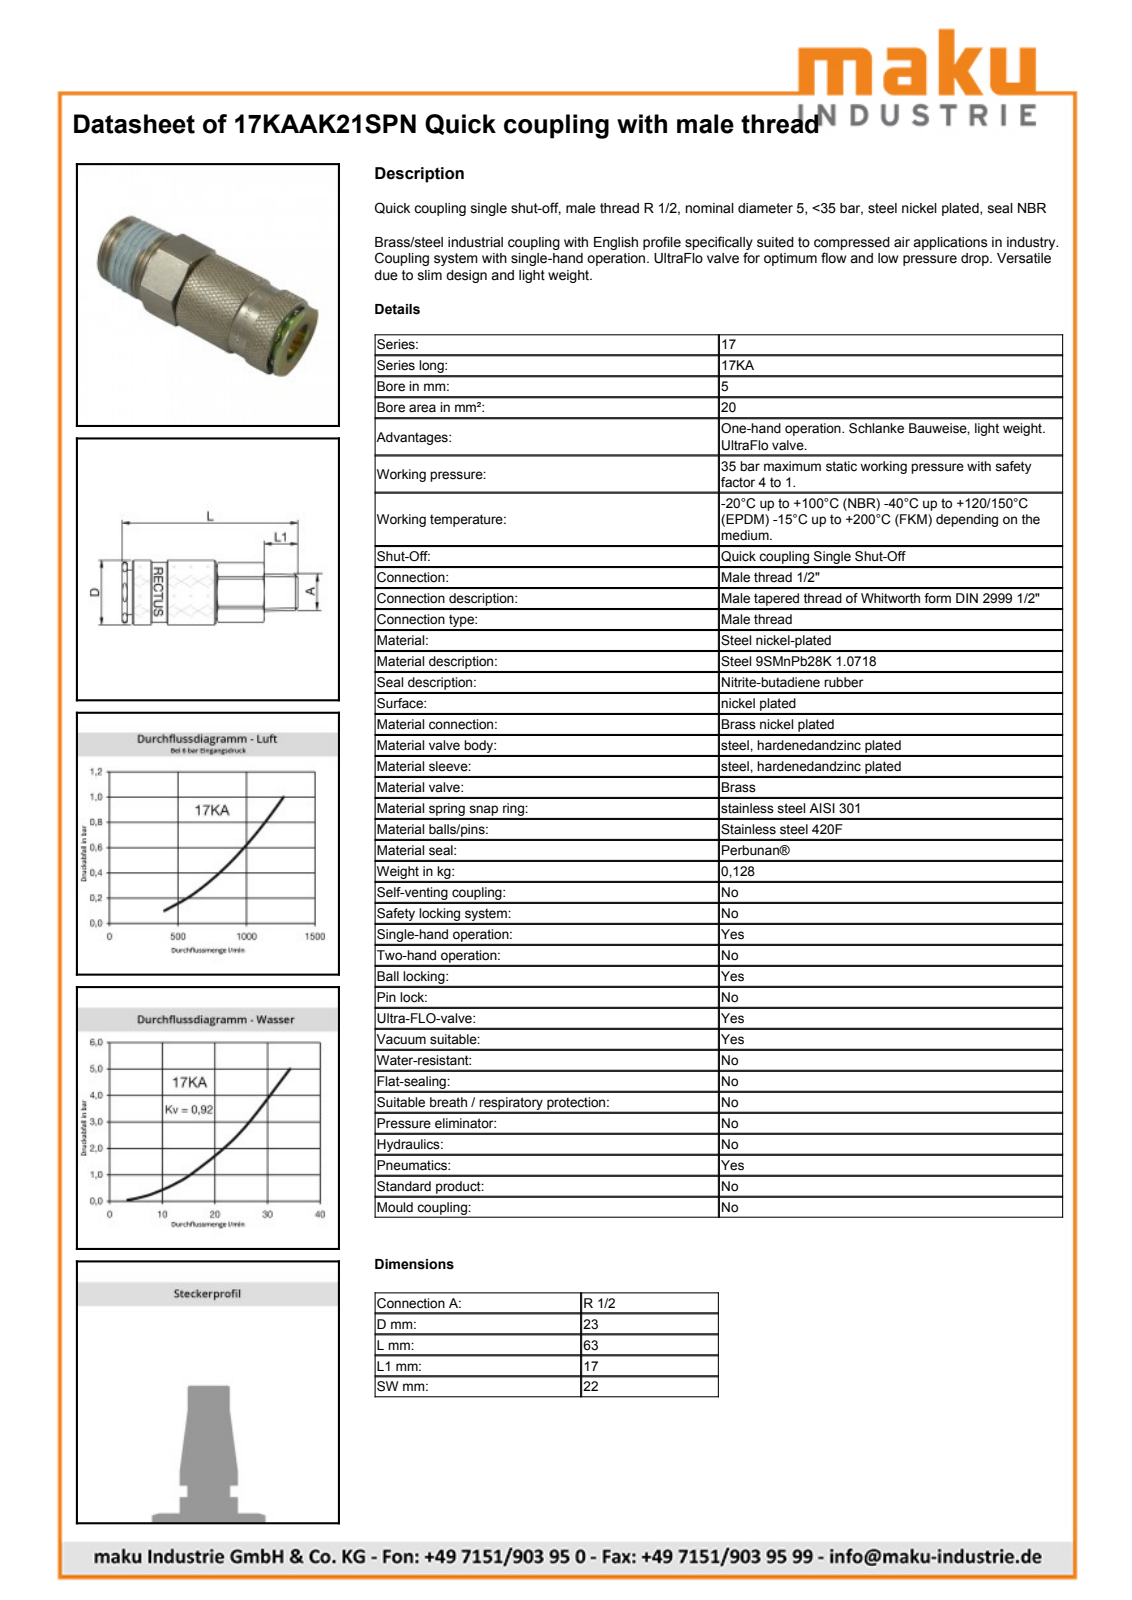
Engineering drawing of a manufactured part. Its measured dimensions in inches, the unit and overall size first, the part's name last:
Units: inches
Overall size (bounding box): 2.457 × 0.976 × 0.911
Round holes (diameter × count): ⌀0.636 ×1, ⌀0.73 ×1, ⌀0.758 ×1
Round bosses / shafts (diameter × count): ⌀0.911 ×1, ⌀0.846 ×1, ⌀0.746 ×1, ⌀0.63 ×1, ⌀0.63 ×1
Partial cylindrical surfaces — rounded edges, fillets, slot ends (radius × count): R0.419 ×1, R0.433 ×1, R0.488 ×1
Main face-to-face distances: 0.866, 2.457, 0.118, 2.339, 0.669, 1.669, 1.315, 1.197, 1.142, 0.071
Volume: 1.424 in³ · Surface area: 14.15 in²
Bodies: 2 solids, 514 faces (212 planar, 59 cylindrical, 243 other)
Part name (STEP PRODUCT): D105955
STEP written by: Autodesk Inventor 2011 (AUTOMOTIVE_DESIGN)
